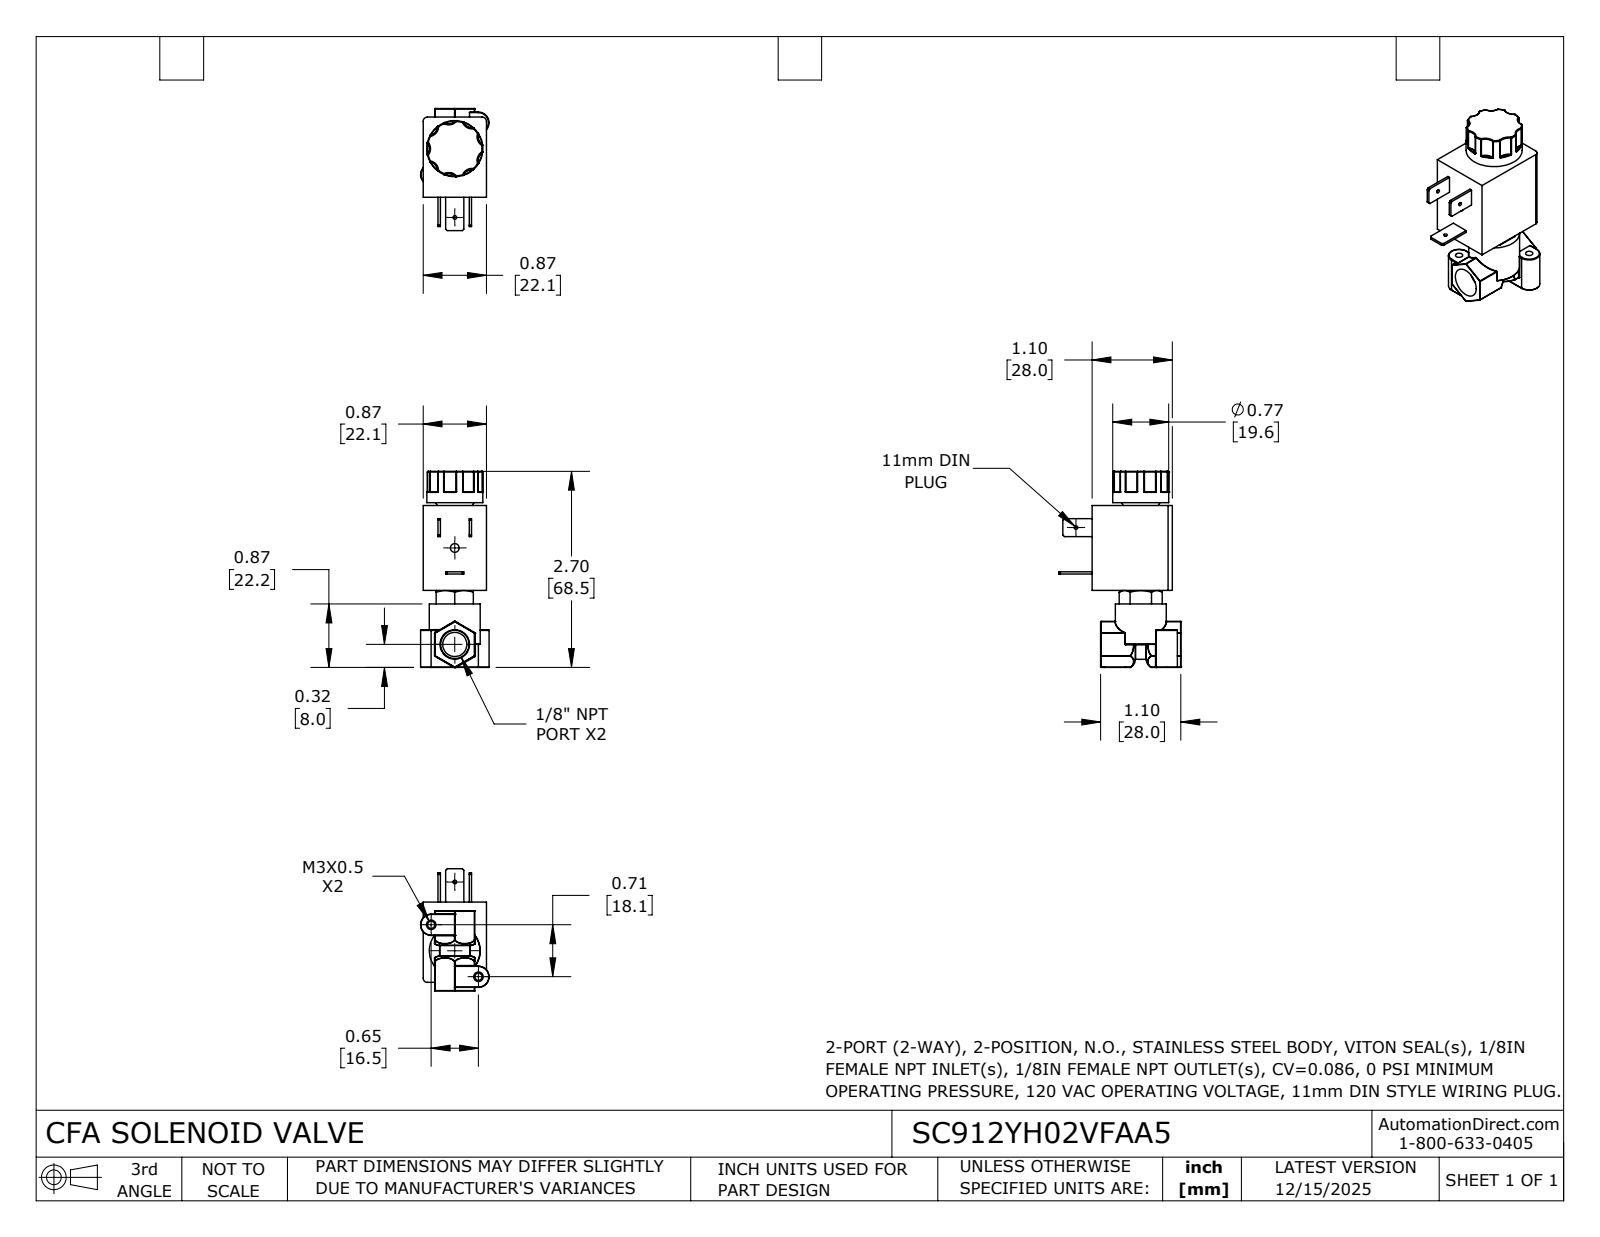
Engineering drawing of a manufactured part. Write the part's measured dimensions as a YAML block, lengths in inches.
part_name: "SC912YH02VFAA5"
step_written_by: "SolidWorks 2024 (CONFIG_CONTROL_DESIGN)"
units: inches
bodies: {solids: 1, faces: 397, planar: 76, cylindrical: 110, other: 211}
overall_size: [2.695, 1.678, 0.942]
volume: 1.739
surface_area: 14.05
round_holes:
  - {diameter: 0.05, count: 2}
  - {diameter: 0.1, count: 2}
  - {diameter: 0.12, count: 1}
  - {diameter: 0.332, count: 1}
round_bosses_or_shafts:
  - {diameter: 0.77, count: 1}
  - {diameter: 0.7, count: 1}
partial_cylinders:
  - {radius: 0.004, count: 29}
  - {radius: 0.01, count: 18}
  - {radius: 0.008, count: 12}
  - {radius: 0.133, count: 7}
  - {radius: 0.017, count: 2}
  - {radius: 0.06, count: 2}
  - {radius: 0.132, count: 2}
  - {radius: 0.146, count: 2}
face_to_face_distances: [0.87, 1.104, 1.167, 1.637, 0.47, 0.548, 0.031, 0.161, 0.709, 1.207]
hole_center_spacings: [0.672, 0.965, 1.326, 1.342]
